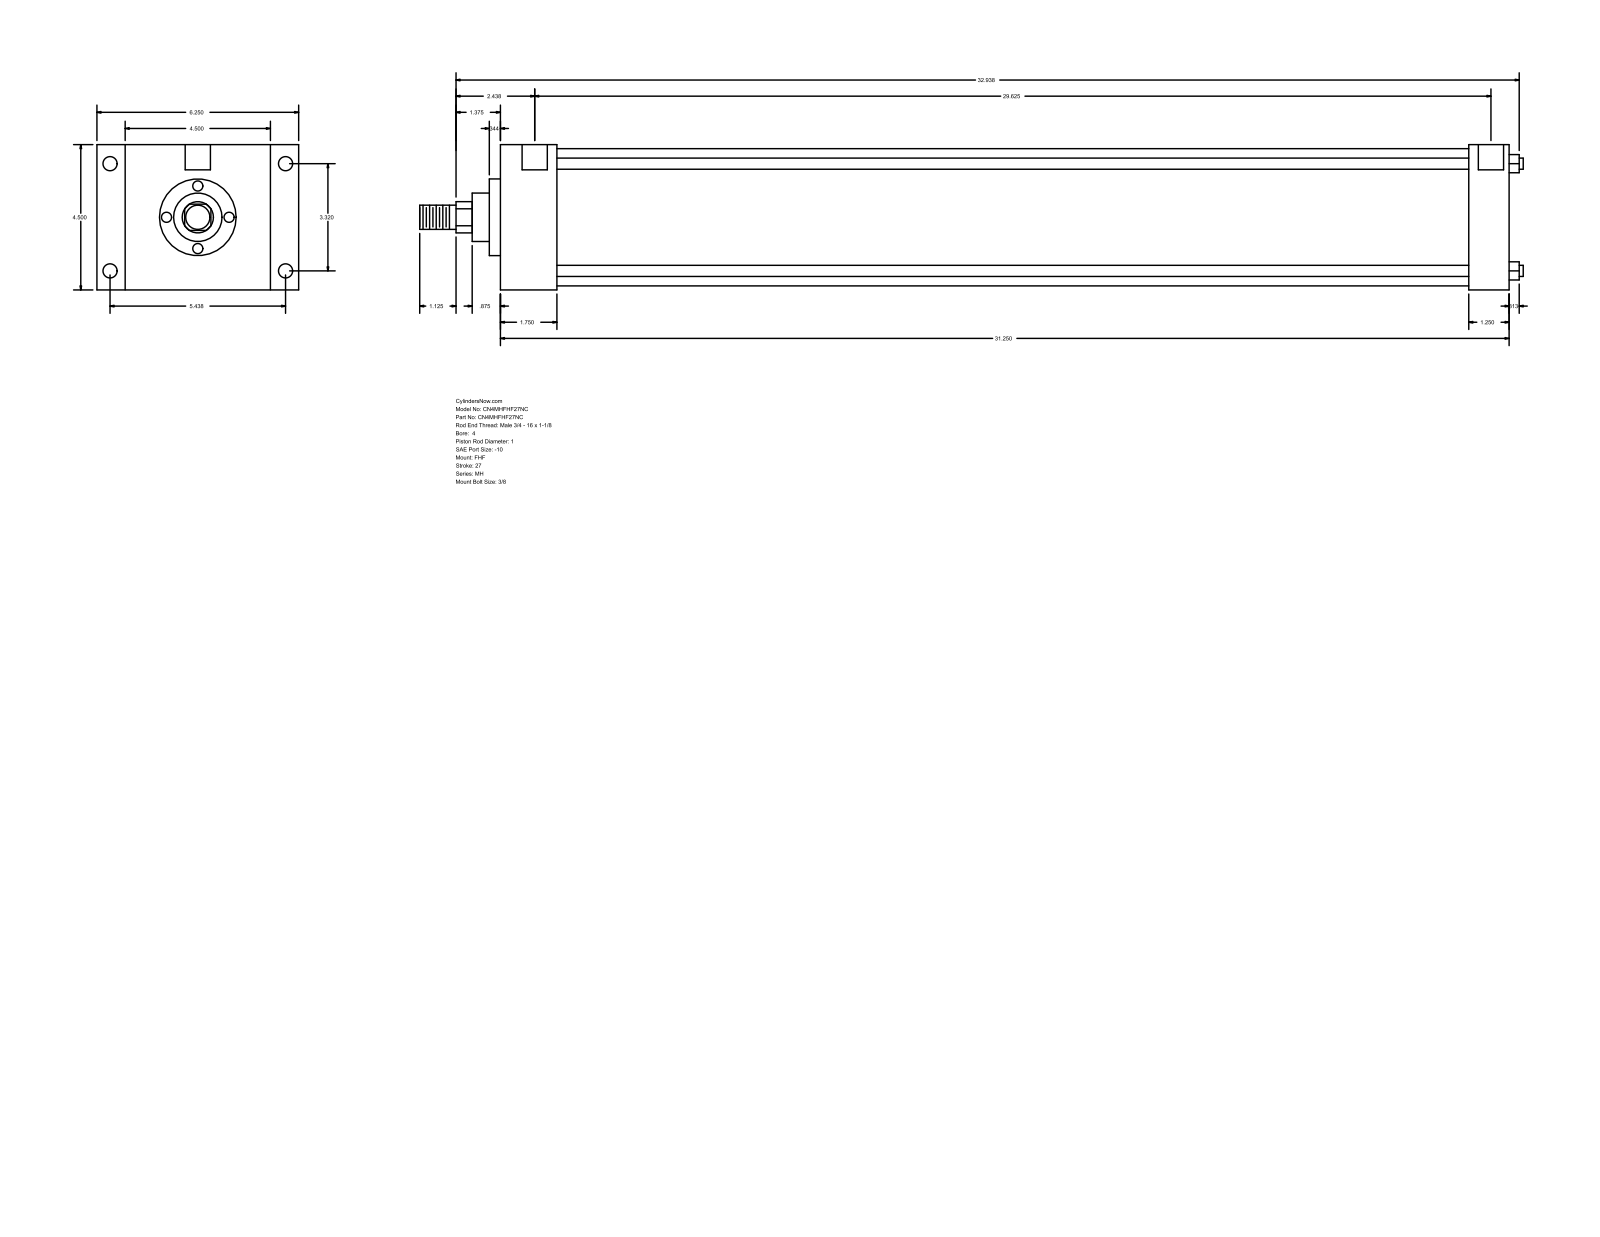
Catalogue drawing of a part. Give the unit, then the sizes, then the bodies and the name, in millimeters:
Units: millimetres
Overall size (bounding box): 868.36 × 158.75 × 114.3
Round holes (diameter × count): ⌀8.73 ×4, ⌀11.13 ×4, ⌀19.84 ×2
Round bosses / shafts (diameter × count): ⌀8.76 ×4, ⌀107.95 ×1, ⌀60.33 ×1, ⌀38.1 ×1, ⌀25.4 ×1, ⌀19.05 ×1
Partial cylindrical surfaces — rounded edges, fillets, slot ends (radius × count): R12.29 ×1
Main face-to-face distances: 114.3, 793.75, 44.46, 749.29, 22.23, 136.53, 158.76, 762, 717.54, 31.75
Hole centre spacings: 84.32, 138.12, 161.82, 755.65, 1.58, 1.59, 752.48, 754.06
Bodies: 0 solids, 90 faces (61 planar, 29 cylindrical, 0 other)
Part name (STEP PRODUCT): MH_FHF__0400_1
STEP written by: GSSL Pune (CONFIG_CONTROL_DESIGN)
